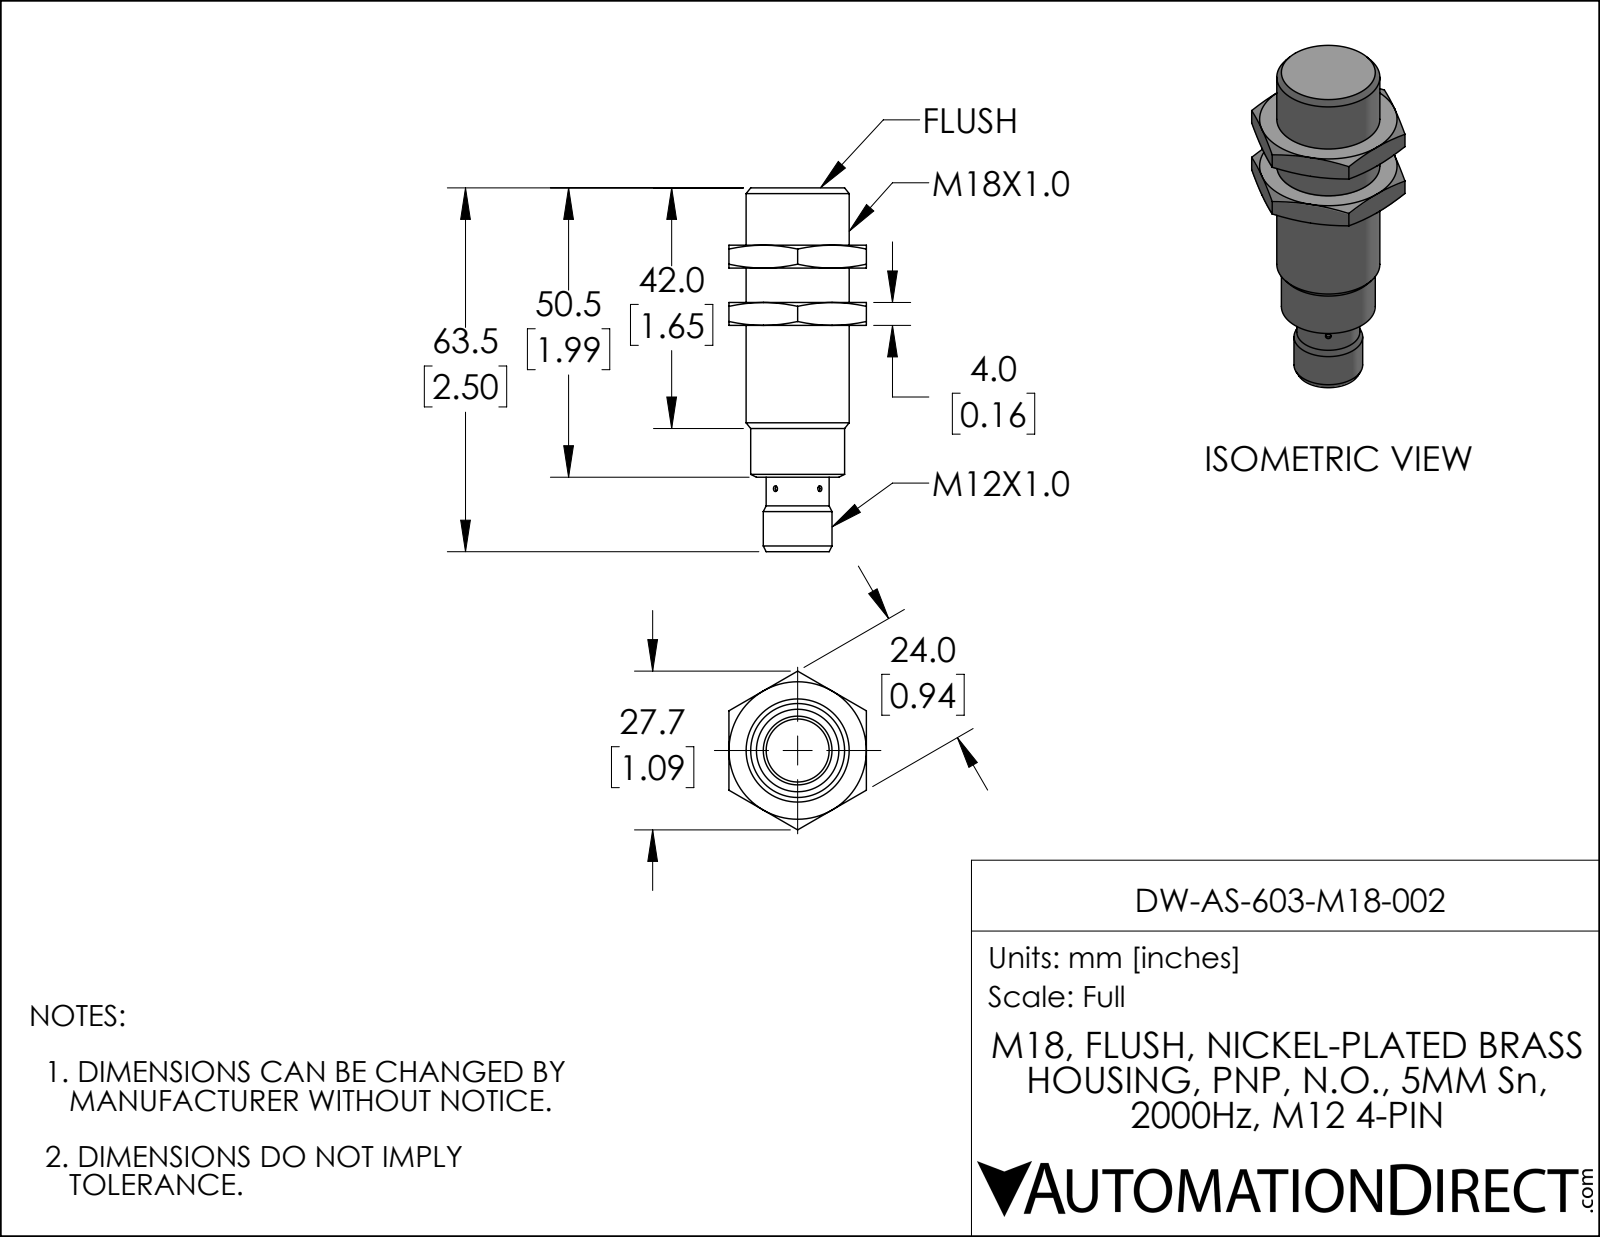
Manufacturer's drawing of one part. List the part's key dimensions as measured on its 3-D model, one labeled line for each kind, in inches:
Part name (STEP PRODUCT): DW-AS-603-M18-002
STEP written by: SolidWorks 2019 (AUTOMOTIVE_DESIGN)
Units: inches
Bodies: 1 solid, 62 faces (23 planar, 10 cylindrical, 29 other)
Overall size (bounding box): 2.5 × 1.091 × 0.945
Volume: 0.958 in³ · Surface area: 7.52 in²
Round holes (diameter × count): ⌀0.039 ×2
Round bosses / shafts (diameter × count): ⌀0.709 ×1, ⌀0.646 ×1, ⌀0.472 ×1, ⌀0.433 ×1
Main face-to-face distances: 0.394, 0.945, 0.551, 0.157, 0.787, 0.236, 2.5, 2.106, 1.949, 1.713
